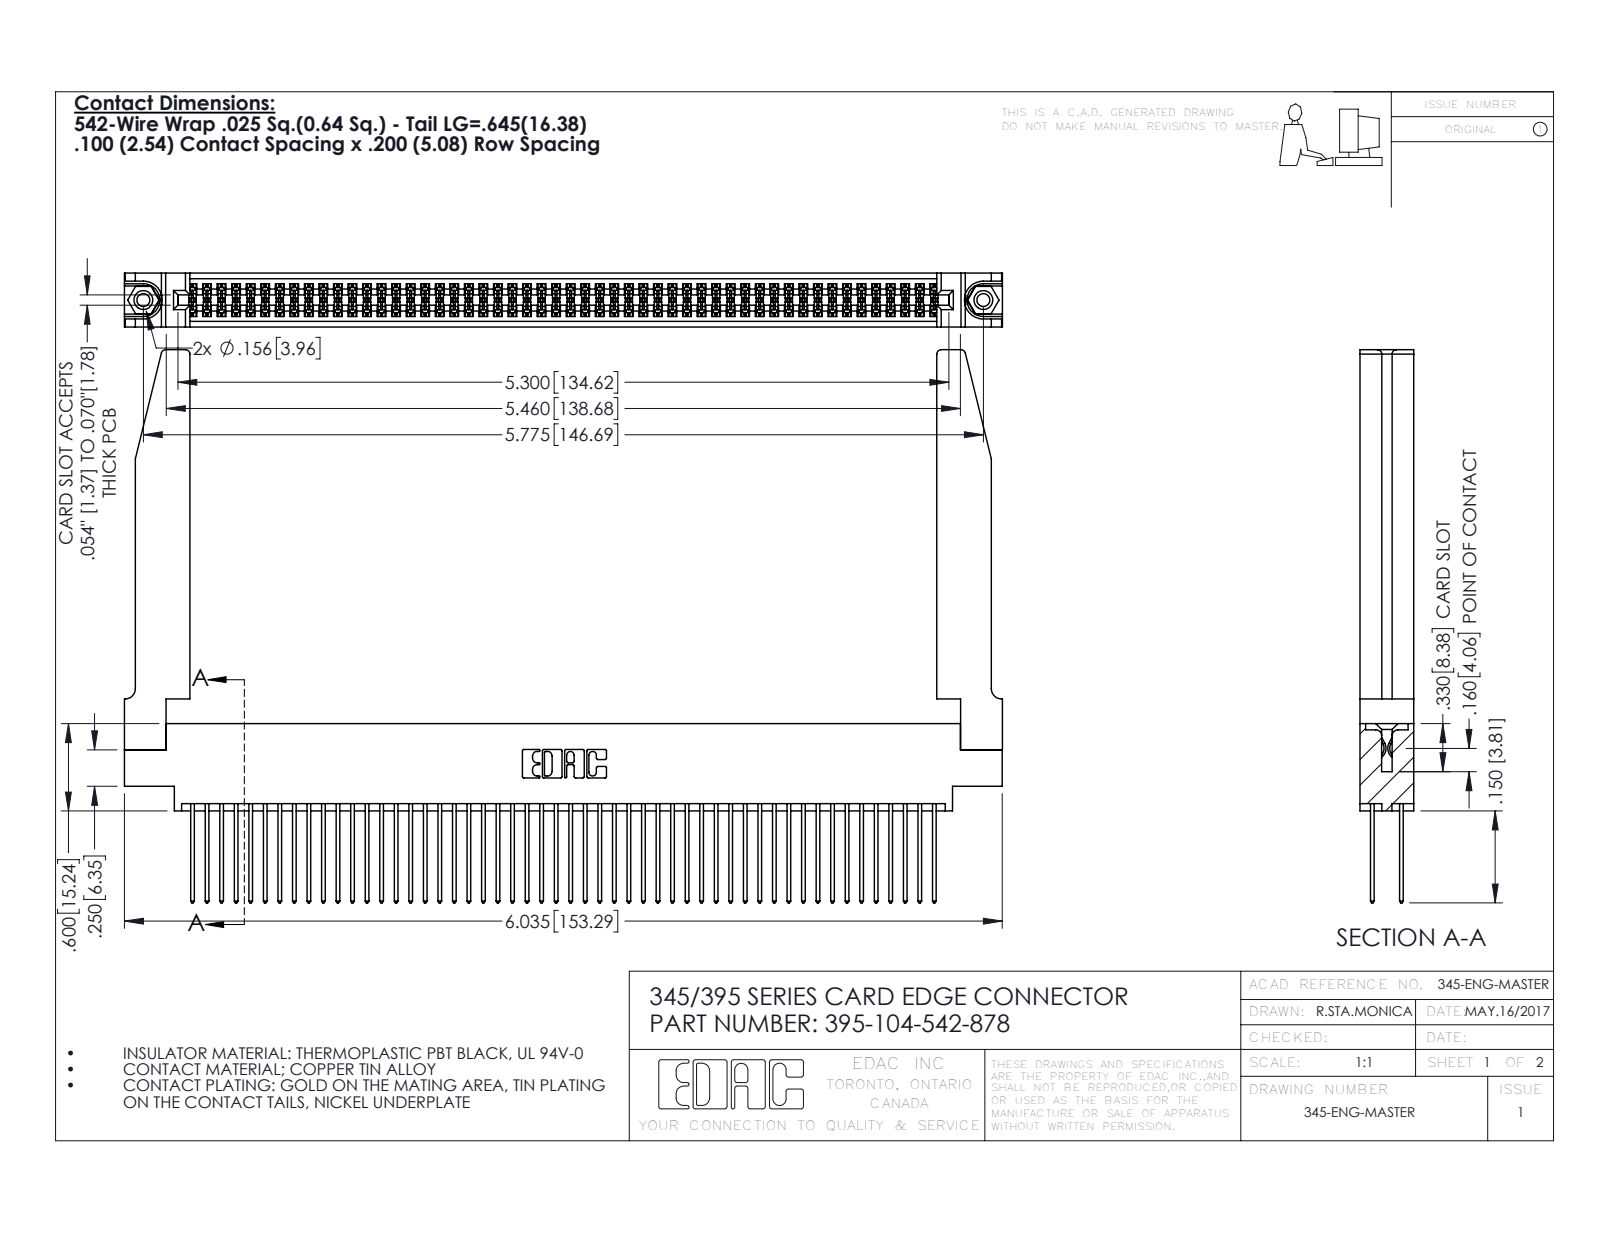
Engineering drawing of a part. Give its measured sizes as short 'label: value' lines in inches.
name: 395-104-542-878; 345-250-001_345-250-001-102; 345-220-078_345-220-078; 345-292-001_345-293-142 (+1 more)
written by: SolidWorks 2016 (CONFIG_CONTROL_DESIGN)
unit: in
bodies: 109 solids, 5564 faces (3658 planar, 1854 cylindrical, 52 other)
size: 6.036 × 3.802 × 0.37
volume: 1.411 in³; area: 49.82 in²
holes: 2× ⌀0.089, 2× ⌀0.125, 2× ⌀0.156, 1× ⌀0.064
bosses: 2× ⌀0.155
rounds: 156× R0.006, 104× R0.01, 22× R0.01, 8× R0.03, 6× R0.007, 6× R0.031, 3× R0.026, 2× R0.014
face distances: 0.072, 0.298, 0.37, 0.098, 0.272, 0.025, 0.2, 0.225, 0.175, 0.15
hole spacings: 0.27, 5.539, 5.775
